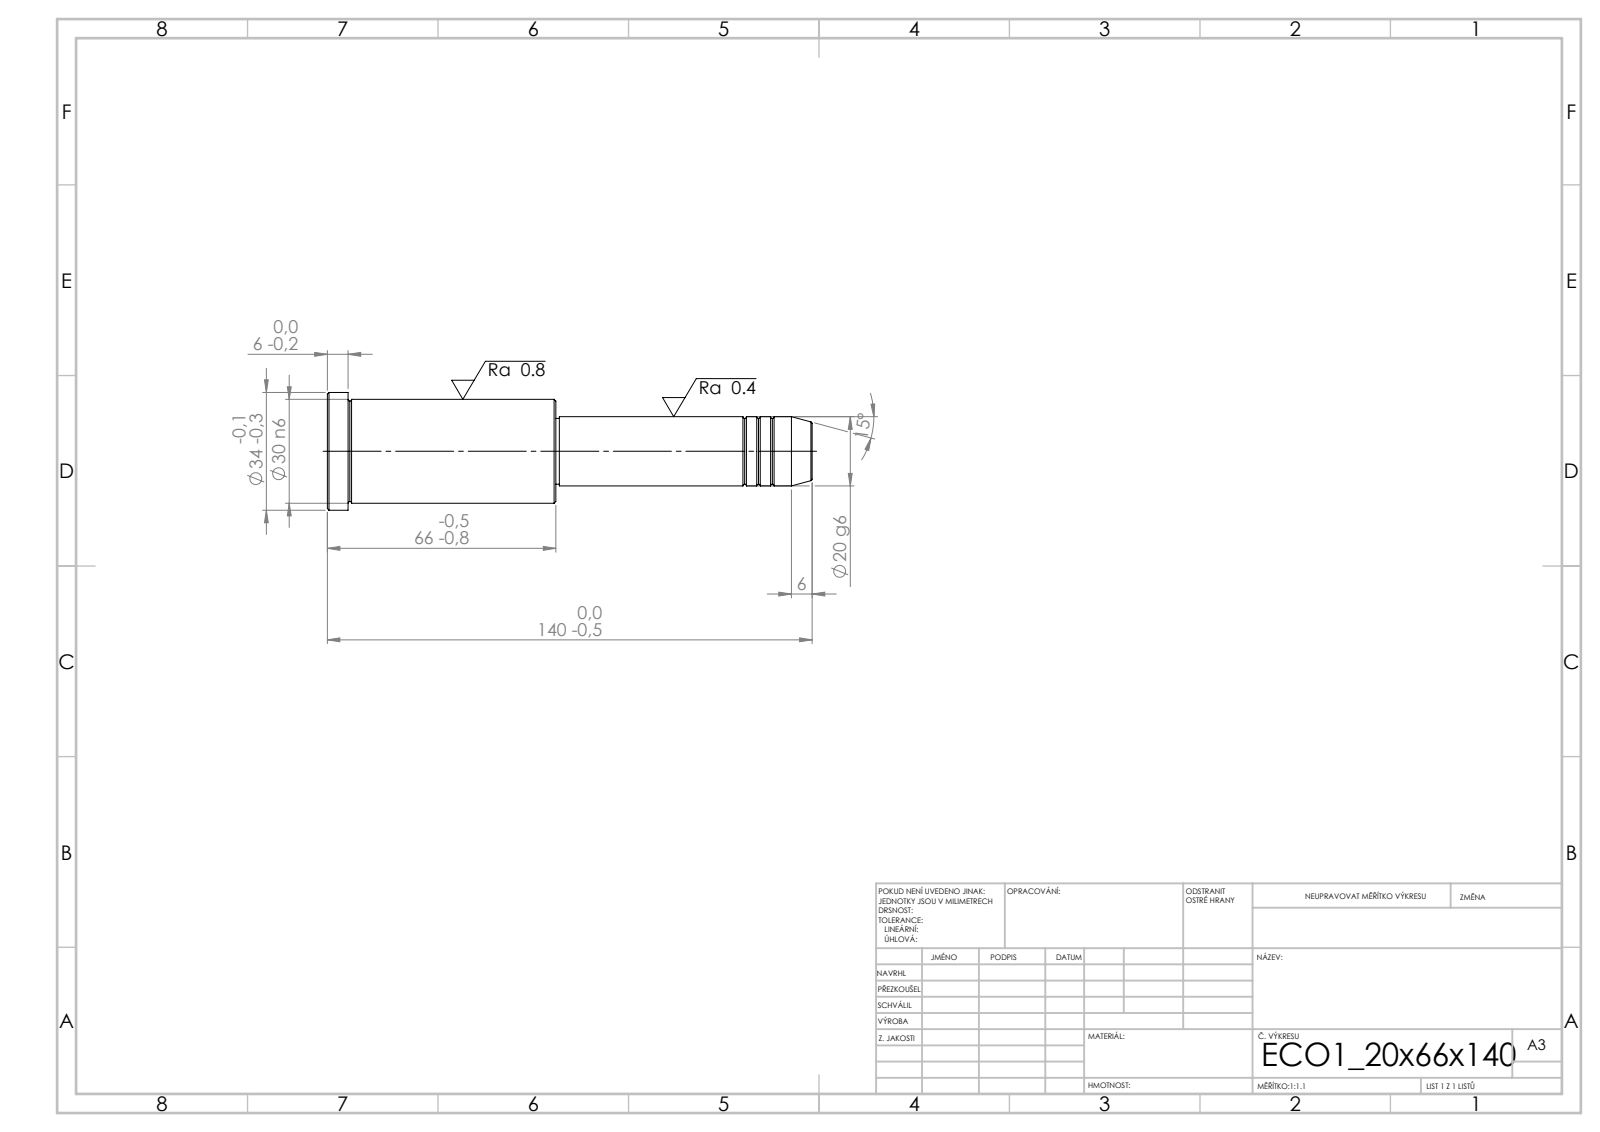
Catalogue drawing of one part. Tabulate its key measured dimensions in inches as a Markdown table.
| quantity | value |
| --- | --- |
| STEP written by | SolidWorks 2019 (CONFIG_CONTROL_DESIGN) |
| units | inches |
| bodies | 1 solid, 43 faces (5 planar, 14 cylindrical, 24 other) |
| overall size | 5.512 × 1.339 × 1.339 |
| volume | 4.312 in³ |
| surface area | 19.83 in² |
| round bosses / shafts (diameter × count) | 1.339 × 1, 1.181 × 1, 0.787 × 1, 0.748 × 1 |
| main face-to-face distances | 2.598, 2.913, 5.512, 5.276, 2.362, 0.236, 2.874, 0.039, 2.402, 2.638 |
